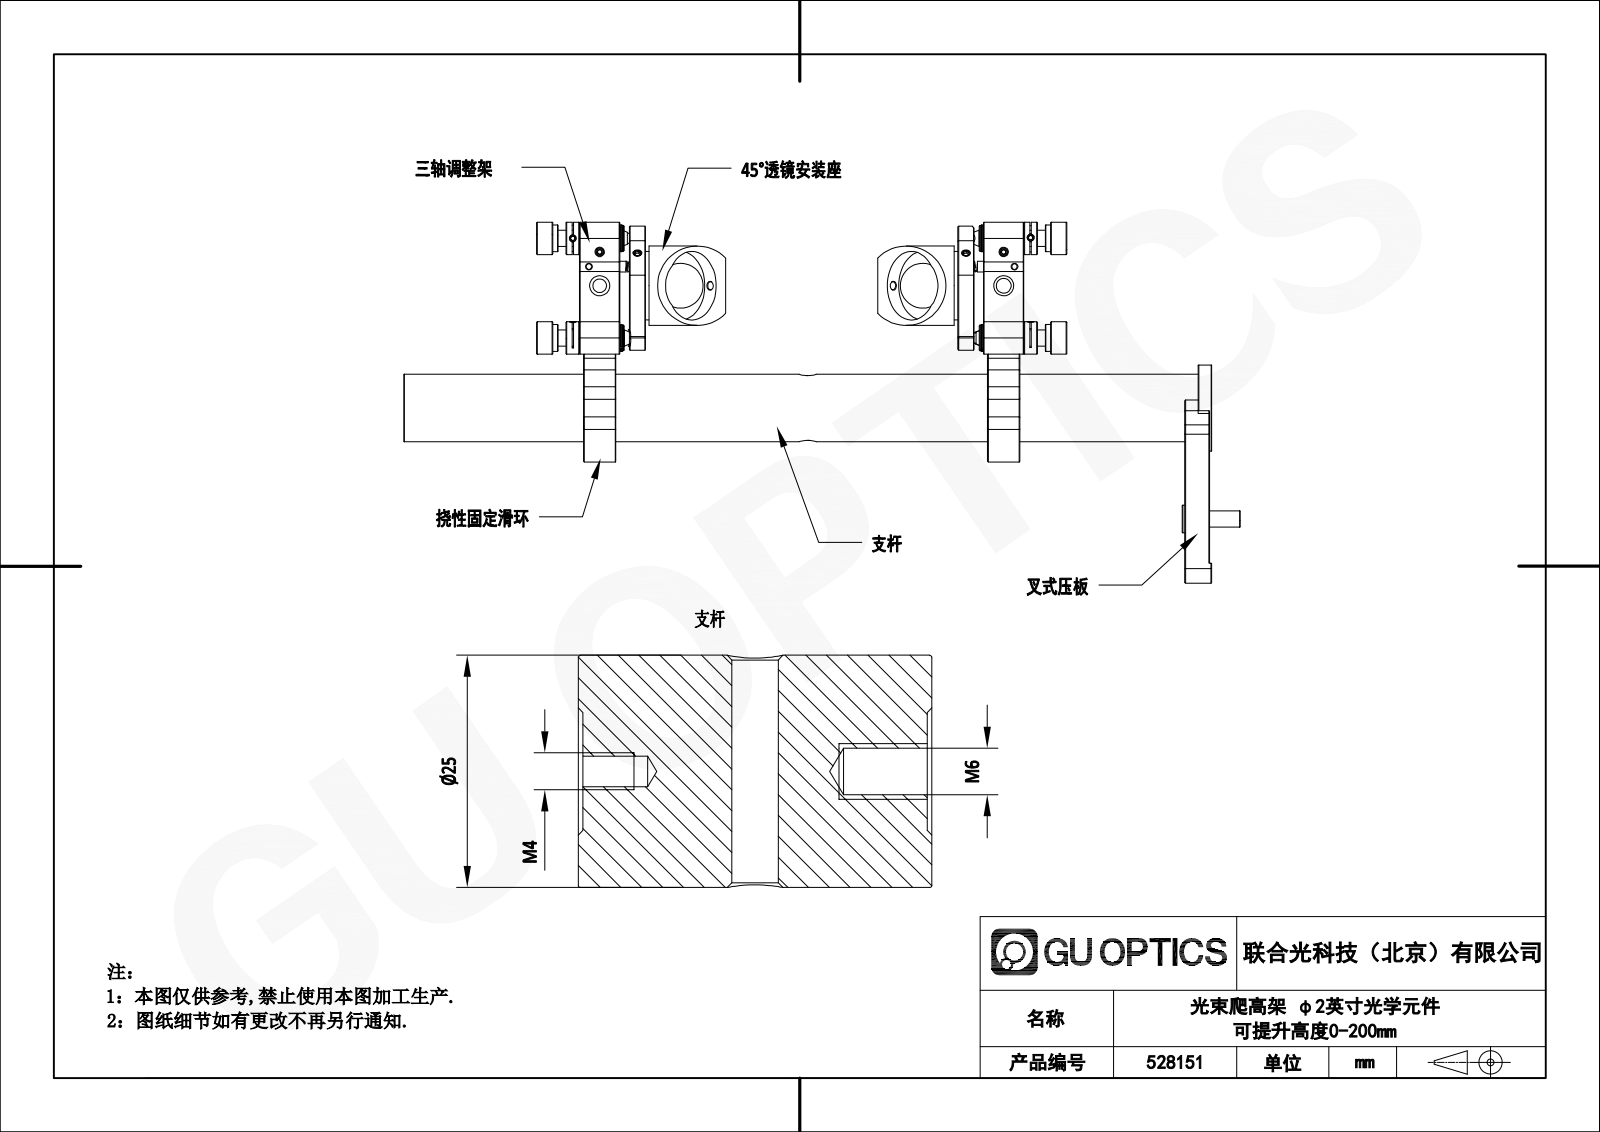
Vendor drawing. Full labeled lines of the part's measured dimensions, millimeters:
Part name (STEP PRODUCT): 528151
STEP written by: SolidWorks 2020 (CONFIG_CONTROL_DESIGN)
Units: millimetres
Bodies: 83 solids, 1623 faces (653 planar, 441 cylindrical, 529 other)
Overall size (bounding box): 310.5 × 158 × 73
Volume: 387 910 mm³ · Surface area: 137 709 mm²
Round holes (diameter × count): ⌀2.5 ×20, ⌀3.3 ×13, ⌀5 ×8, ⌀6 ×7, ⌀7.5 ×4, ⌀3.99 ×3, ⌀4 ×3, ⌀6.5 ×3, ⌀35 ×3, ⌀4.5 ×2, ⌀2 ×1, ⌀6.4 ×1
Round bosses / shafts (diameter × count): ⌀3 ×24, ⌀4 ×11, ⌀12 ×3, ⌀10 ×3, ⌀9.5 ×3, ⌀8 ×3, ⌀7.2 ×3, ⌀58 ×1
Partial cylindrical surfaces — rounded edges, fillets, slot ends (radius × count): R0.2 ×72, R5 ×18, R0.5 ×12, R2 ×10, R4 ×10, R1 ×8, R6 ×3, R26.4 ×3
Main face-to-face distances: 12, 165.12, 1, 199.12, 1.5, 30.5, 17, 182.12, 13.5, 153.12
Hole centre spacings: 15.89, 203.21, 10.83, 25.75, 31, 41.4, 200.78, 202.88
